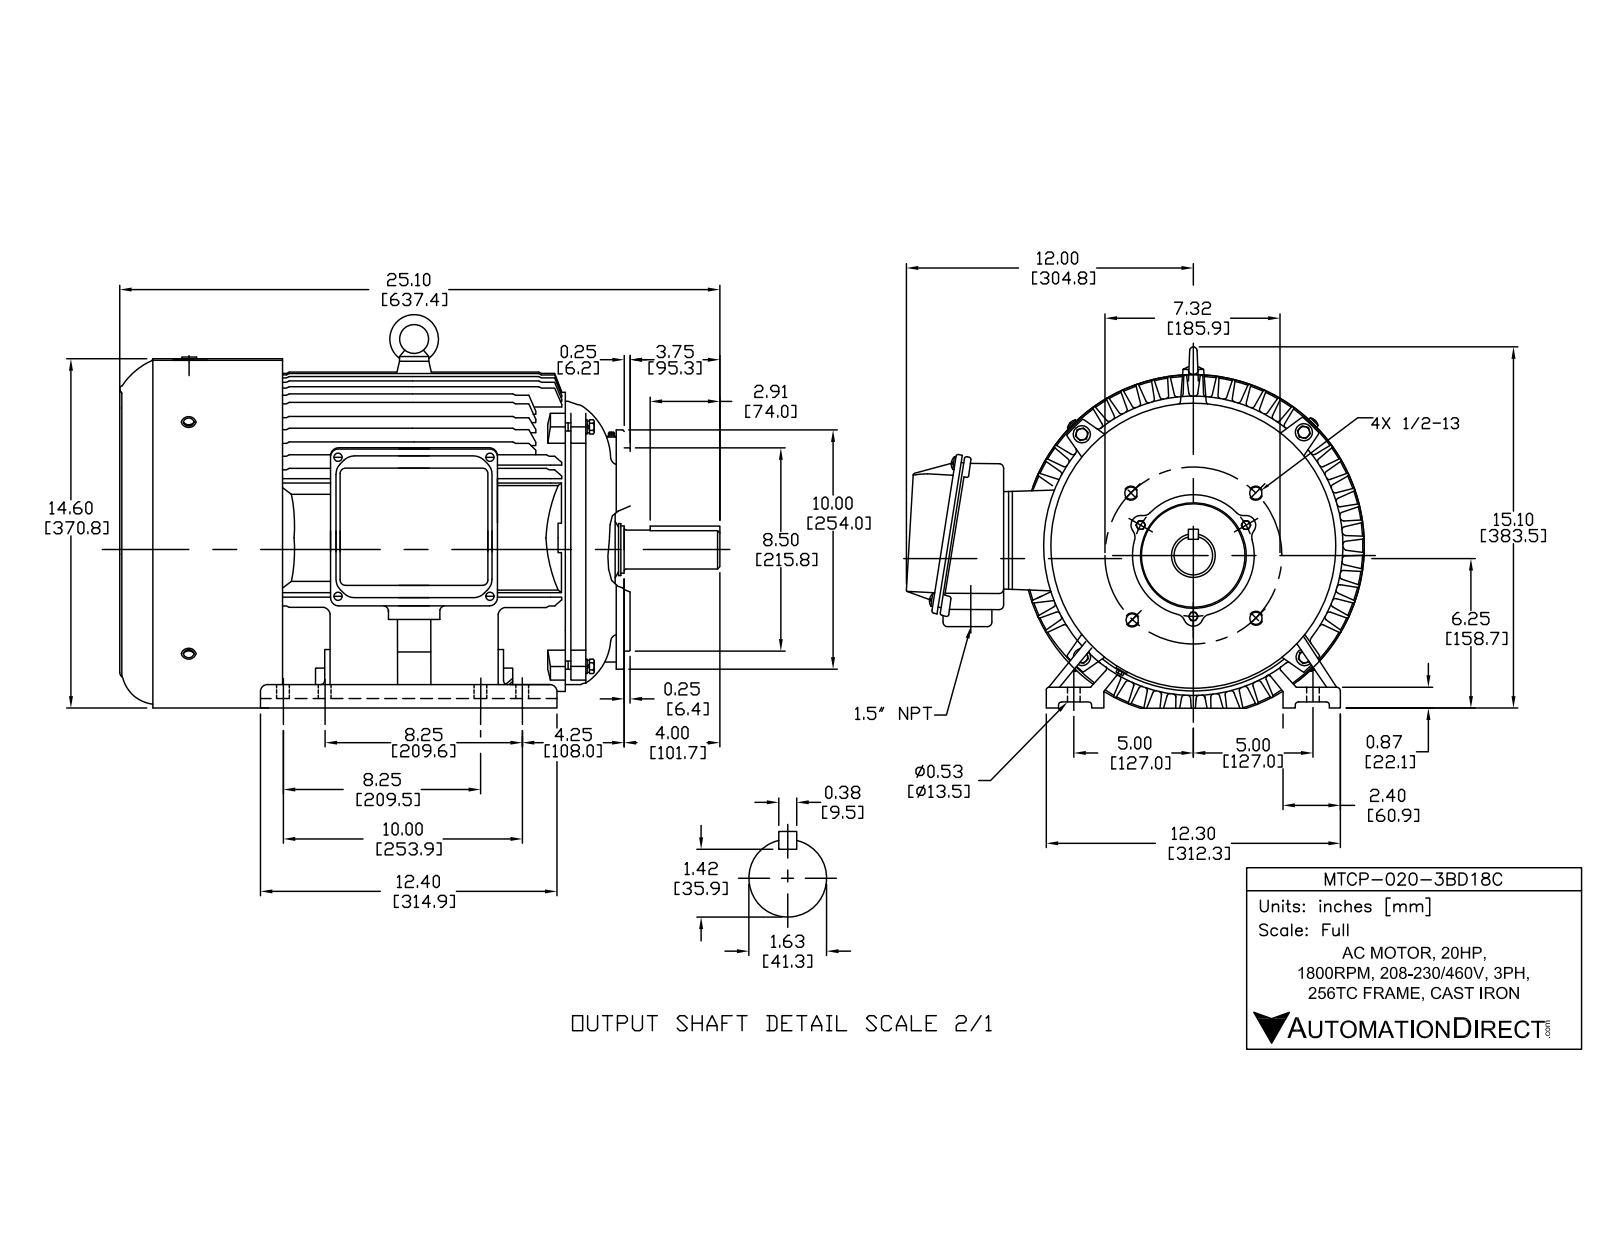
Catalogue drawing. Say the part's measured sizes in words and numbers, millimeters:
The part is named "17橡皮塞; spring lock washers--normal type gb_GB_FASTENER_WASHER_SW 6; PE250前轴承外盖加工件; hex head bolts-full thread grade c gb_GB_FASTENER_BOLT_HHBFTC M6X16-N (+8 more)". Its 3-D file was written by "SolidWorks 2017 (AUTOMOTIVE_DESIGN)". It is 67 solids with 3495 faces: 907 planar, 1314 cylindrical and 1274 other. Overall it measures 642.9 by 469.92 by 397.85 millimeters. Its volume is 9 814 000 cubic millimeters and its surface area 2 541 000 square millimeters. Round holes: 14 of diameter 7, 12 of diameter 5, 9 of diameter 17, 8 of diameter 8, 8 of diameter 10.72, 4 of diameter 2.05, 4 of diameter 6.4, 4 of diameter 6.68, 4 of diameter 8.5, 4 of diameter 9, 4 of diameter 10.5, 4 of diameter 10.9. Round bosses or shafts: 11 of diameter 6, 5 of diameter 12, 5 of diameter 10, 4 of diameter 20, 4 of diameter 16.1, 4 of diameter 9.88, 2 of diameter 5, 1 of diameter 355. Partial cylindrical surfaces (rounded edges, fillets, slot ends): 259 of radius 1, 80 of radius 5, 72 of radius 3, 48 of radius 0.5, 38 of radius 4, 36 of radius 1.5, 26 of radius 8, 20 of radius 10. The main face-to-face distances are 5, 1.5, 17, 33, 513.8, 512.3, 10, 77.94, 22, 23. The hole center spacings are 75, 57.5, 70.47, 116.73, 186.34, 74.99, 92.08, 106.06.
